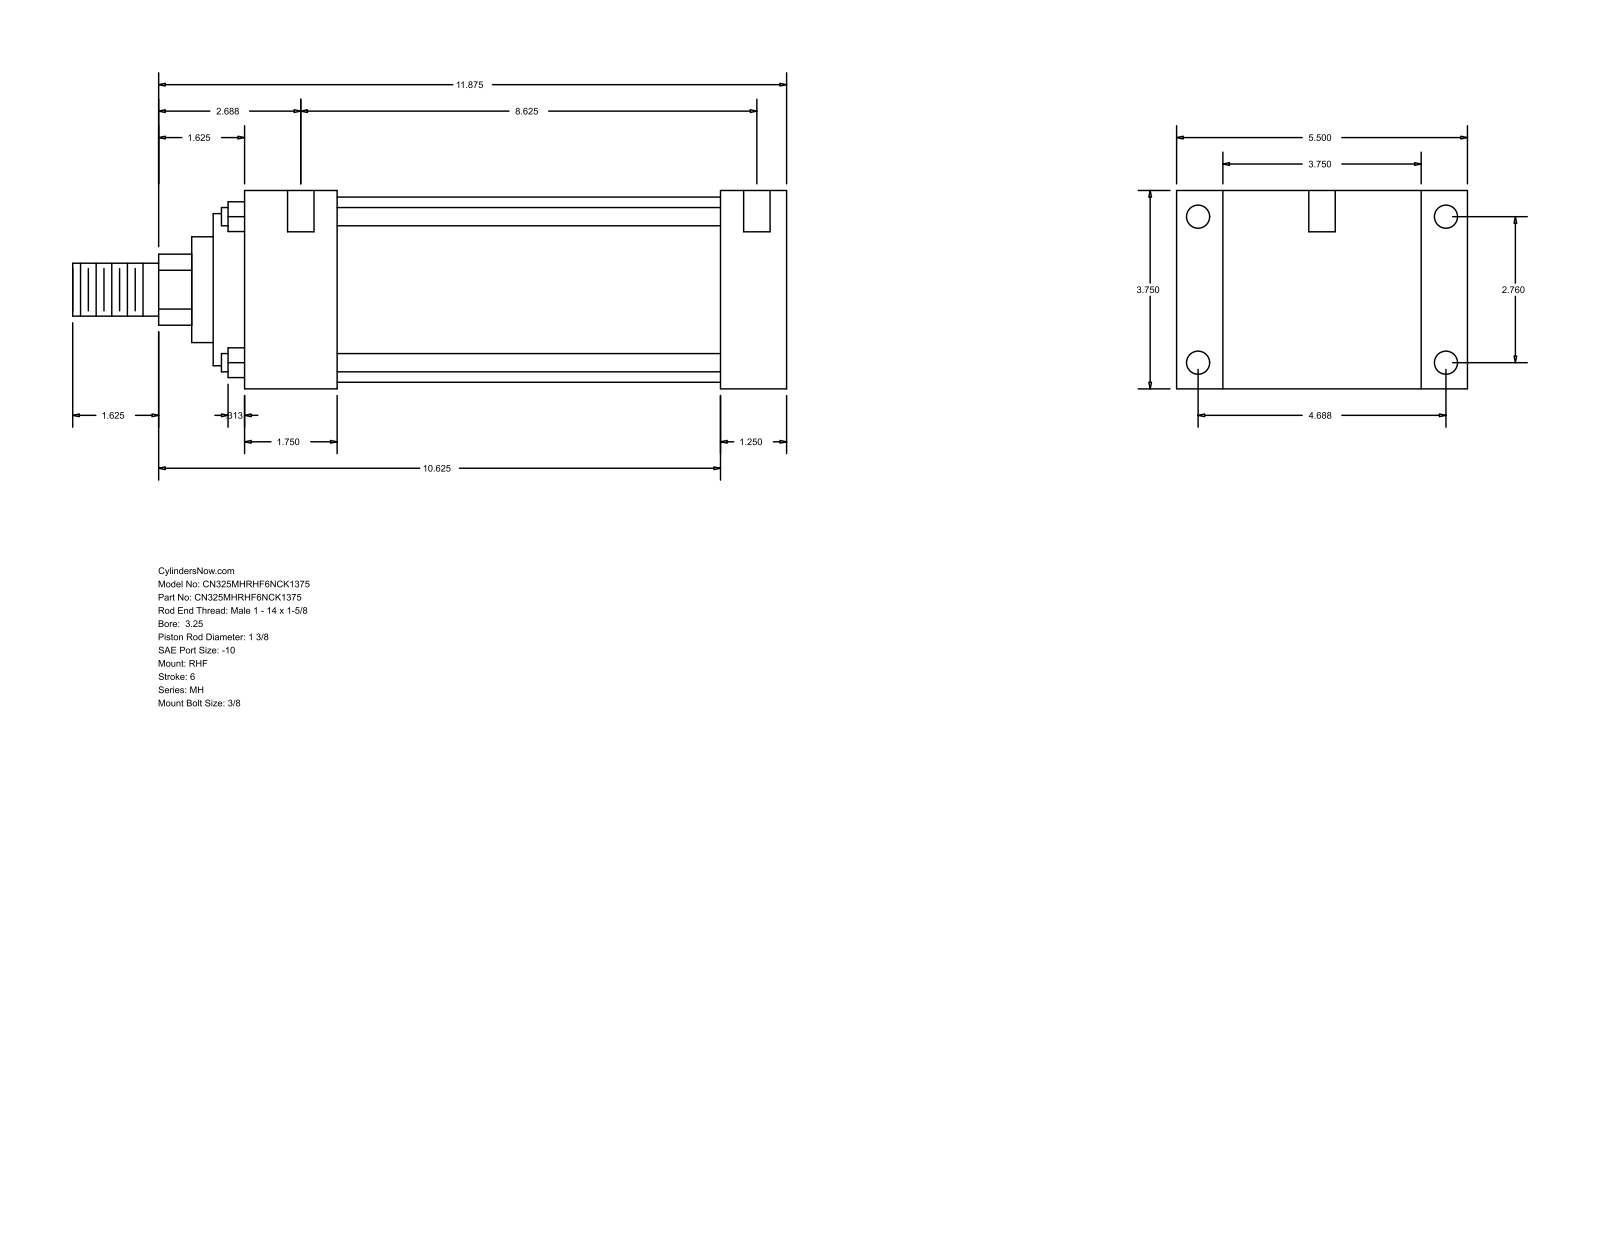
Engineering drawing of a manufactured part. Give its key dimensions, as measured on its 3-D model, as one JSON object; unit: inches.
{"part_name": "MH_RHF__0325_1.375", "step_written_by": "GSSL Pune (CONFIG_CONTROL_DESIGN)", "units": "inches", "bodies": {"solids": 0, "faces": 90, "planar": 61, "cylindrical": 29, "other": 0}, "overall_size": [13.5, 5.5, 3.75], "round_holes": [[0.219, 4], [0.438, 4], [0.5, 2]], "round_bosses_or_shafts": [[0.345, 4], [3.5, 1], [2.875, 1], [2, 1], [1.375, 1], [1, 1]], "partial_cylinders_radius": [[0.672, 1]], "face_to_face_distances": [3.75, 1.25, 0.875, 4.625, 9, 10.25, 5.5, 1.75, 7.25, 8.5], "hole_center_spacings": [2.76, 4.687, 5.439, 8.875, 0.063, 0.187, 8.625, 8.688]}
